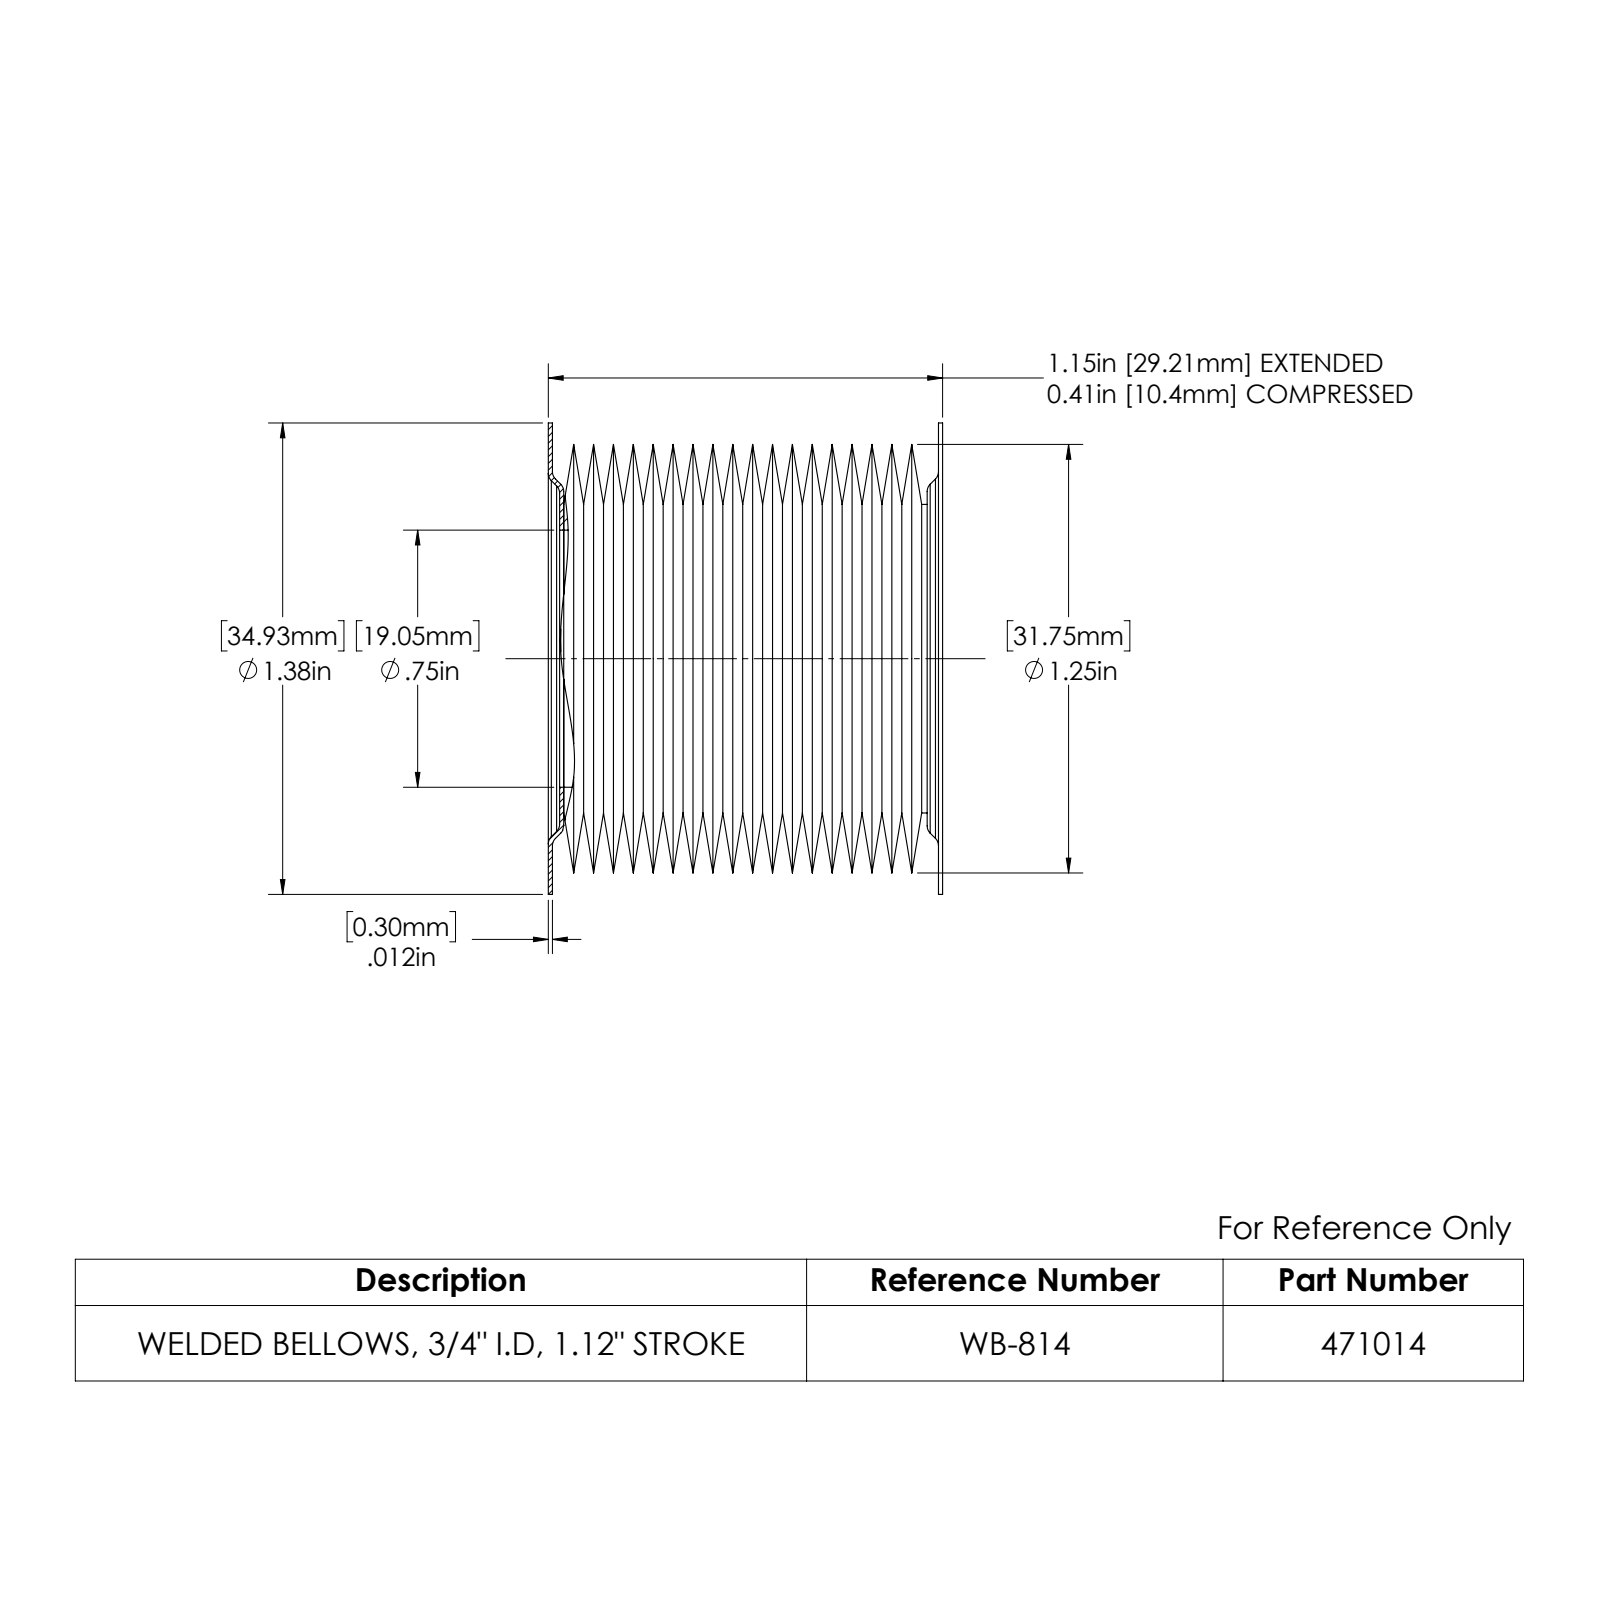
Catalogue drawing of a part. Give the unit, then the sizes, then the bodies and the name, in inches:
Units: inches
Overall size (bounding box): 1.375 × 1.375 × 1.15
Round holes (diameter × count): ⌀0.75 ×1
Round bosses / shafts (diameter × count): ⌀1.375 ×1, ⌀0.9 ×1
Main face-to-face distances: 1.105, 0.033, 1.138, 0.045, 1.093, 1.117, 0.021, 1.15, 1.126, 1.072
Volume: 0.524 in³ · Surface area: 28.59 in²
Bodies: 2 solids, 115 faces (9 planar, 10 cylindrical, 96 other)
Part name (STEP PRODUCT): 471014
STEP written by: SolidWorks 2022 (AUTOMOTIVE_DESIGN)
